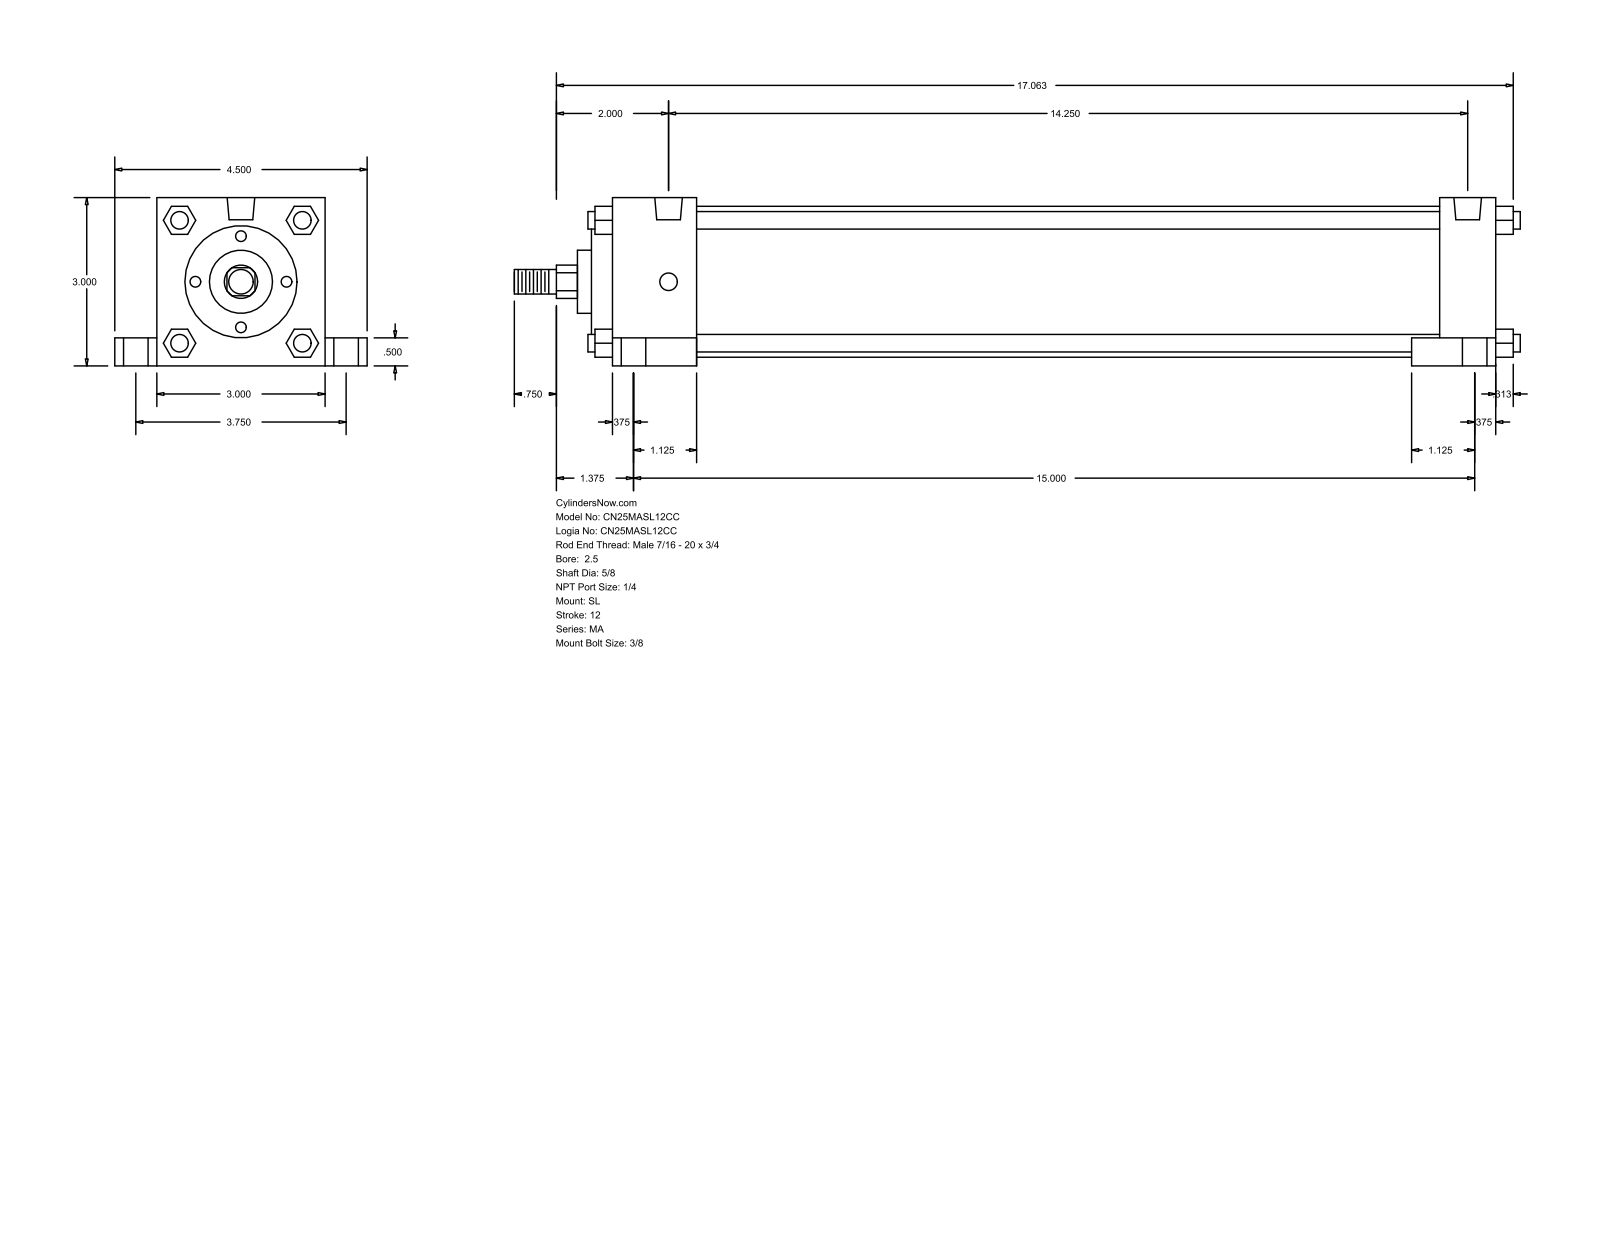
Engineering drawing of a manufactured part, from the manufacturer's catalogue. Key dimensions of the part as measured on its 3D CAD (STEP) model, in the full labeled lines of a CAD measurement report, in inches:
Part name (STEP PRODUCT): MA_SL__0250_0.625
STEP written by: GSSL Pune (CONFIG_CONTROL_DESIGN)
Units: inches
Bodies: 0 solids, 150 faces (113 planar, 37 cylindrical, 0 other)
Overall size (bounding box): 17.937 × 4.5 × 3
Round holes (diameter × count): ⌀0.313 ×4, ⌀0.437 ×4, ⌀0.687 ×4, ⌀0.492 ×2
Round bosses / shafts (diameter × count): ⌀0.313 ×4, ⌀2.69 ×1, ⌀2 ×1, ⌀1.125 ×1, ⌀0.625 ×1, ⌀0.437 ×1
Partial cylindrical surfaces — rounded edges, fillets, slot ends (radius × count): R0.297 ×1
Main face-to-face distances: 3, 15.75, 0.5, 13.25, 1, 1.5, 14.25, 14.75, 0.75, 2.5
Hole centre spacings: 1.879, 1.976, 3.75, 14.25, 14.497, 14.993, 15, 15.462
